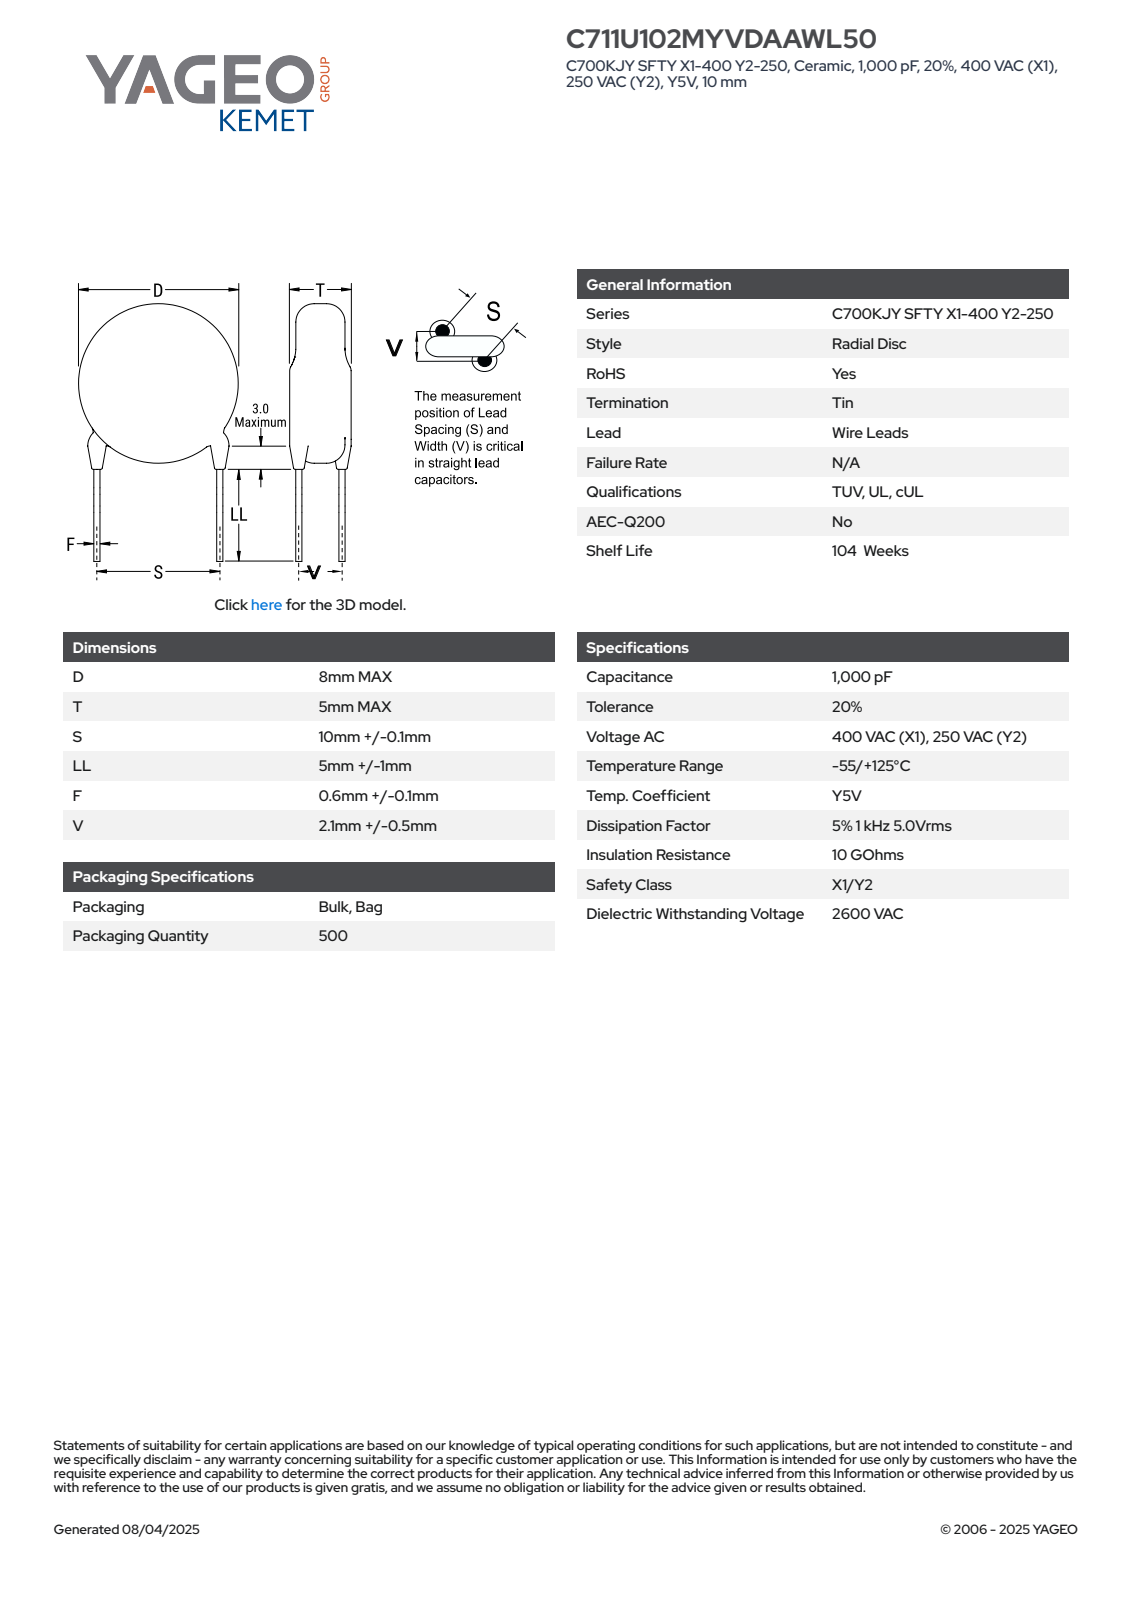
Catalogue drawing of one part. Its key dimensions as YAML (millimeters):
part_name: "CCD_KST_8X5_D8T5S11LL6F0.7V2.1"
step_written_by: "SolidWorks 2021 (AUTOMOTIVE_DESIGN)"
units: millimeters
bodies: {solids: 4, faces: 81, planar: 63, cylindrical: 14, other: 4}
overall_size: [15.5, 11.2, 5]
volume: 256
surface_area: 271
round_bosses_or_shafts:
  - {diameter: 1.2, count: 4}
  - {diameter: 0.7, count: 2}
  - {diameter: 8, count: 1}
face_to_face_distances: [5, 6, 0.97, 12.02, 6.02, 11.05, 5.05, 0.36, 0.78, 3.96]
